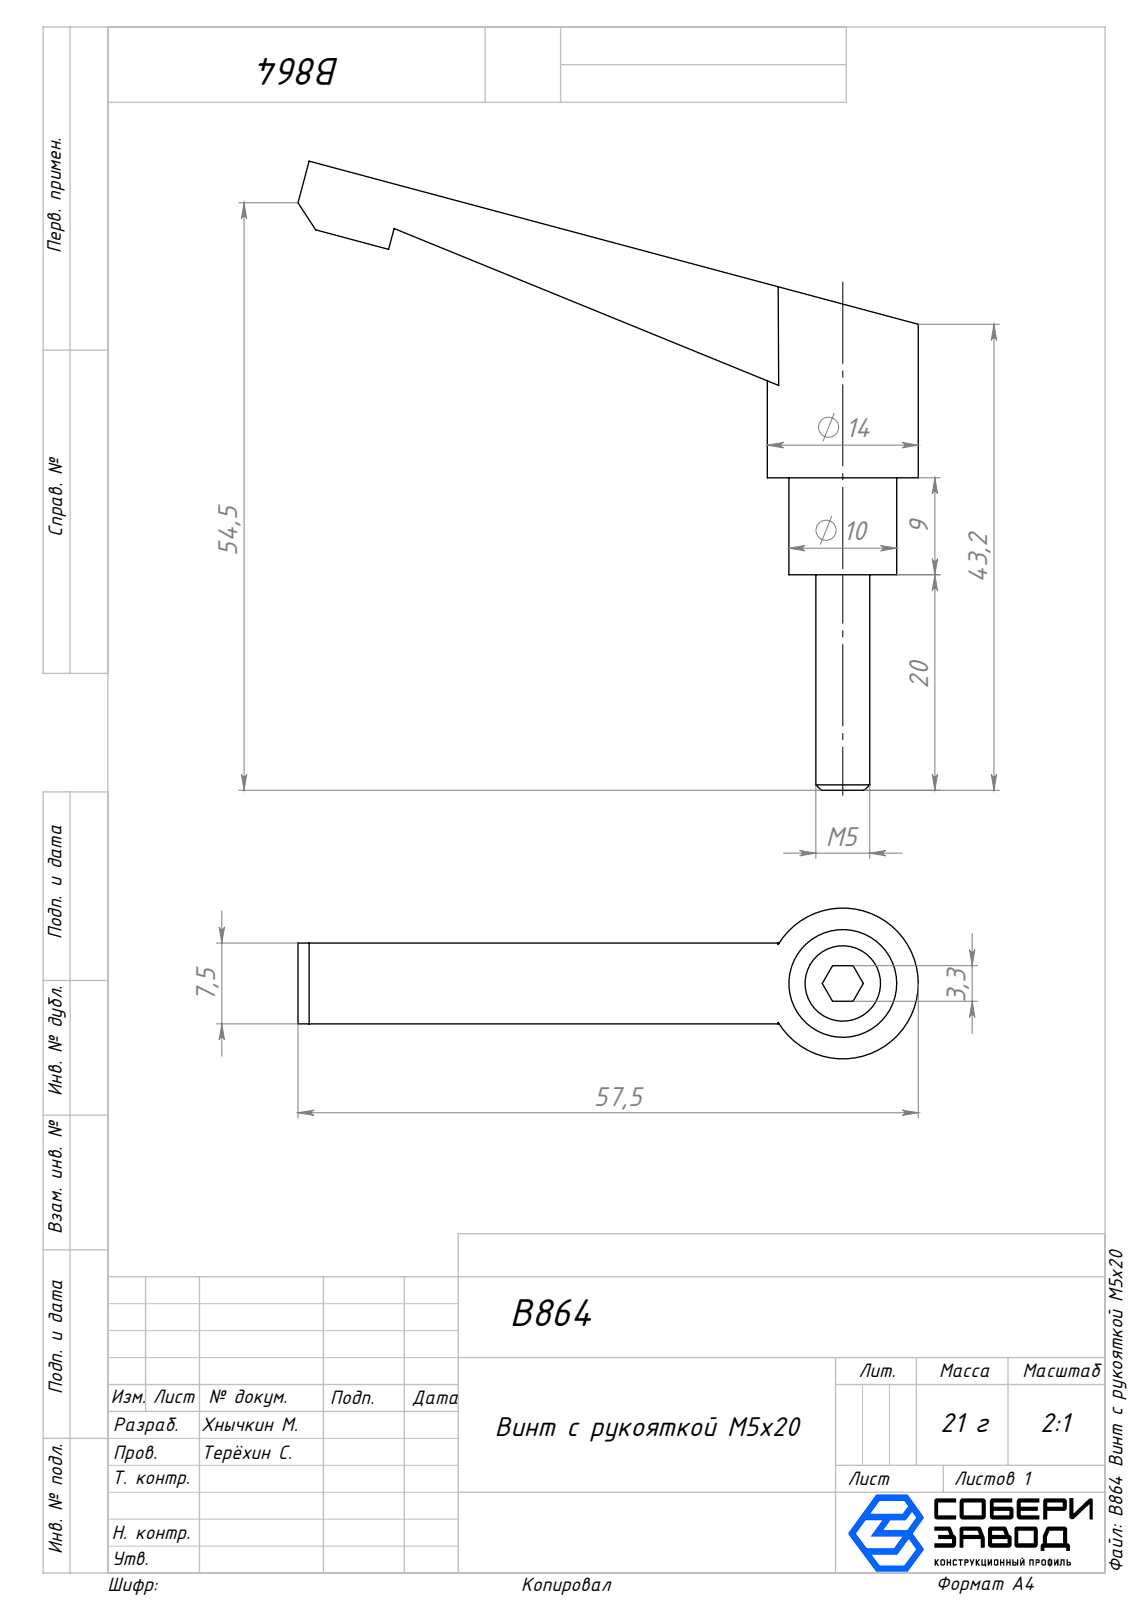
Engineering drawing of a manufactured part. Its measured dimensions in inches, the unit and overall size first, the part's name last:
Units: inches
Overall size (bounding box): 2.299 × 2.265 × 0.551
Round holes (diameter × count): ⌀0.118 ×1, ⌀0.236 ×1, ⌀0.394 ×1
Round bosses / shafts (diameter × count): ⌀0.551 ×1, ⌀0.276 ×1, ⌀0.197 ×1
Main face-to-face distances: 0.039, 0.295, 0.256, 0.217, 0.138, 0.394, 0.433, 0.787, 0.354, 0.748
Volume: 0.286 in³ · Surface area: 6.87 in²
Bodies: 3 solids, 52 faces (32 planar, 18 cylindrical, 2 other)
Part name (STEP PRODUCT): Винтик_00; Рукоятка_00; B864 Винт с рукояткой М5х20; Винт с рукояткой_00
STEP written by: SolidWorks 2025 (AUTOMOTIVE_DESIGN)
